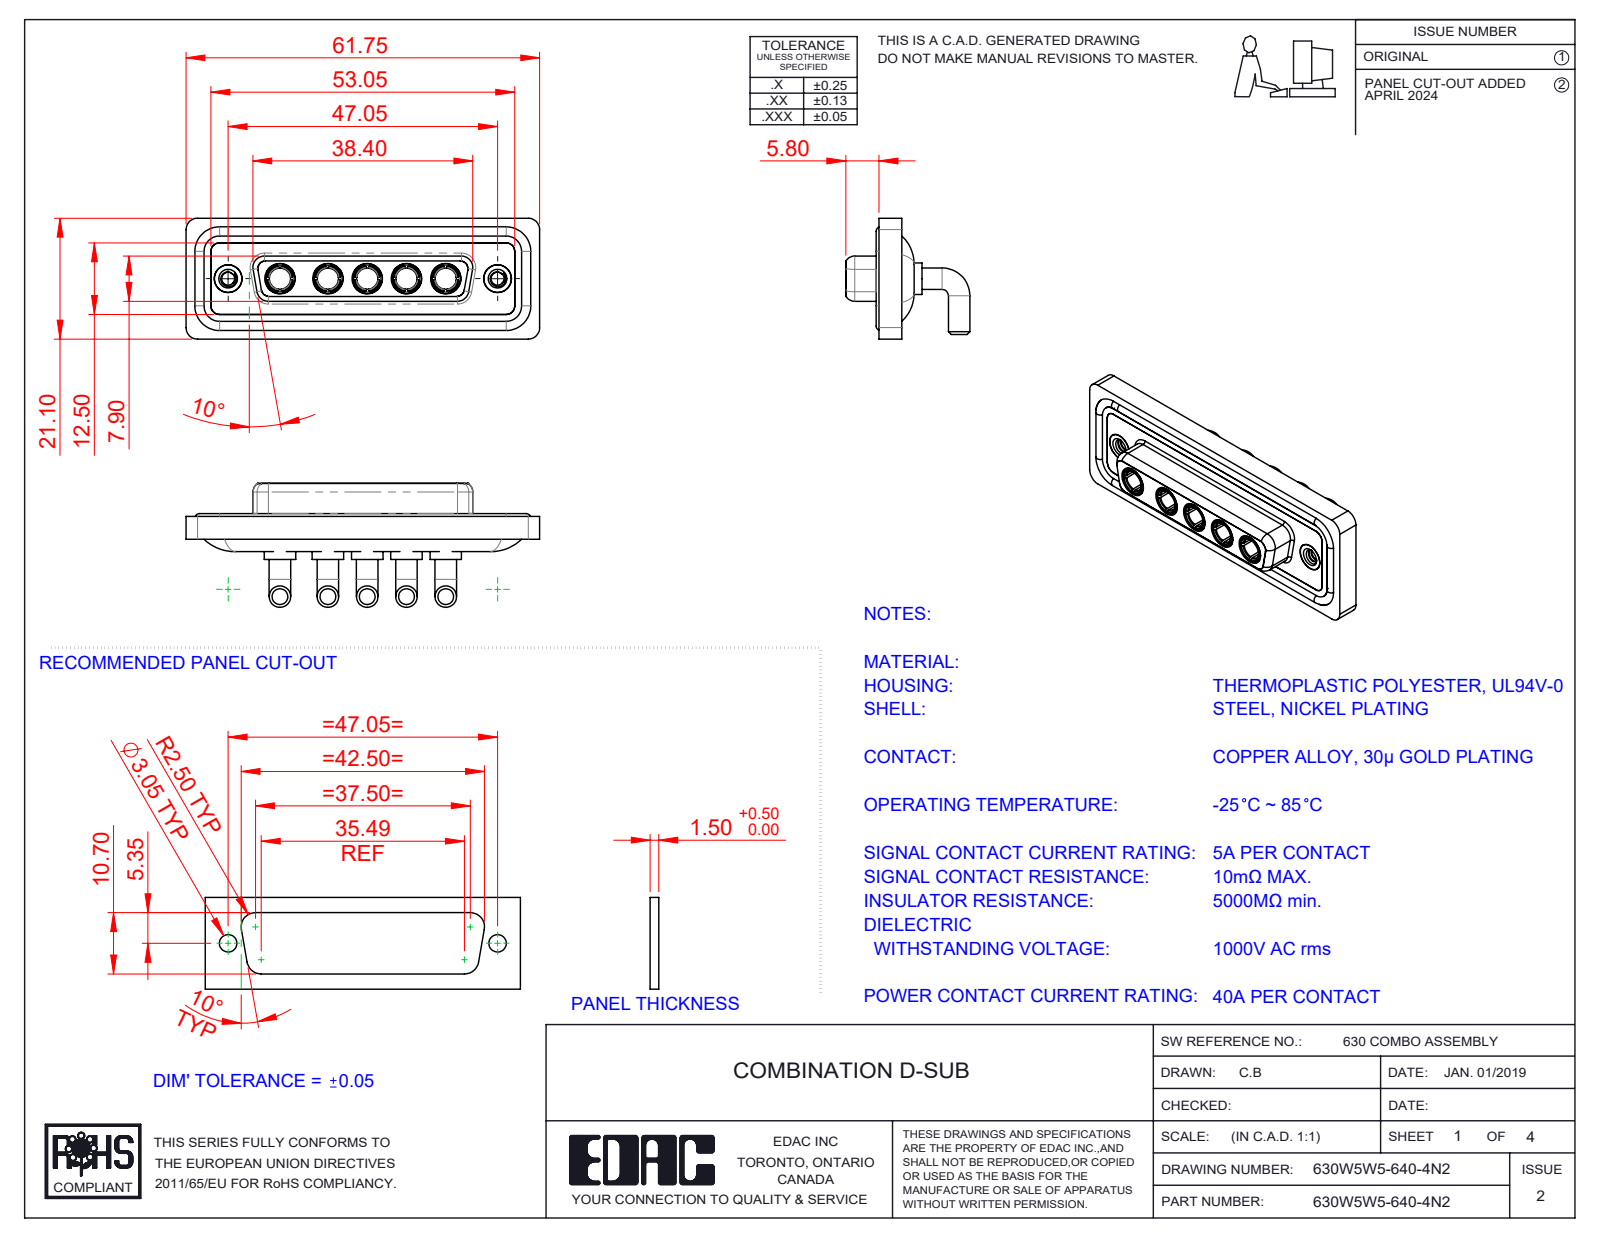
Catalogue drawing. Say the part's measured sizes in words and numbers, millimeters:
The part is named "630Combo Housing_5W5; 630Combo Shell Front_25 Contacts; 630Combo Shell Rear_25 Contacts; Power Socket_40A RA (+3 more)". Its 3-D file was written by "SolidWorks 2023 (CONFIG_CONTROL_DESIGN)". It is 17 solids with 776 faces: 250 planar, 313 cylindrical and 213 other. Overall it measures 61.75 by 21.68 by 21.1 millimeters. Its volume is 8 799 cubic millimeters and its surface area 14 032 square millimeters. Round holes: 7 of diameter 4.85, 5 of diameter 3.7, 5 of diameter 5.3, 2 of diameter 2.26, 2 of diameter 4, 2 of diameter 4.05, 2 of diameter 5. Round bosses or shafts: 10 of diameter 3.75, 5 of diameter 5.5, 5 of diameter 5.2, 5 of diameter 4.96, 5 of diameter 4.75, 4 of diameter 1.6, 2 of diameter 4.95, 2 of diameter 4.8. Partial cylindrical surfaces (rounded edges, fillets, slot ends): 18 of radius 1.5, 18 of radius 2, 8 of radius 1.35, 8 of radius 1.6, 5 of radius 2.1, 4 of radius 0.25, 4 of radius 0.5, 4 of radius 0.6. The main face-to-face distances are 0.4, 1.8, 4.1, 1.1, 2.5, 3.1, 3.7, 1.6, 1.5, 2.9. The hole center spacings are 6.86, 9.04, 38.01, 6.87, 8.38, 13.72, 13.73, 15.25.
